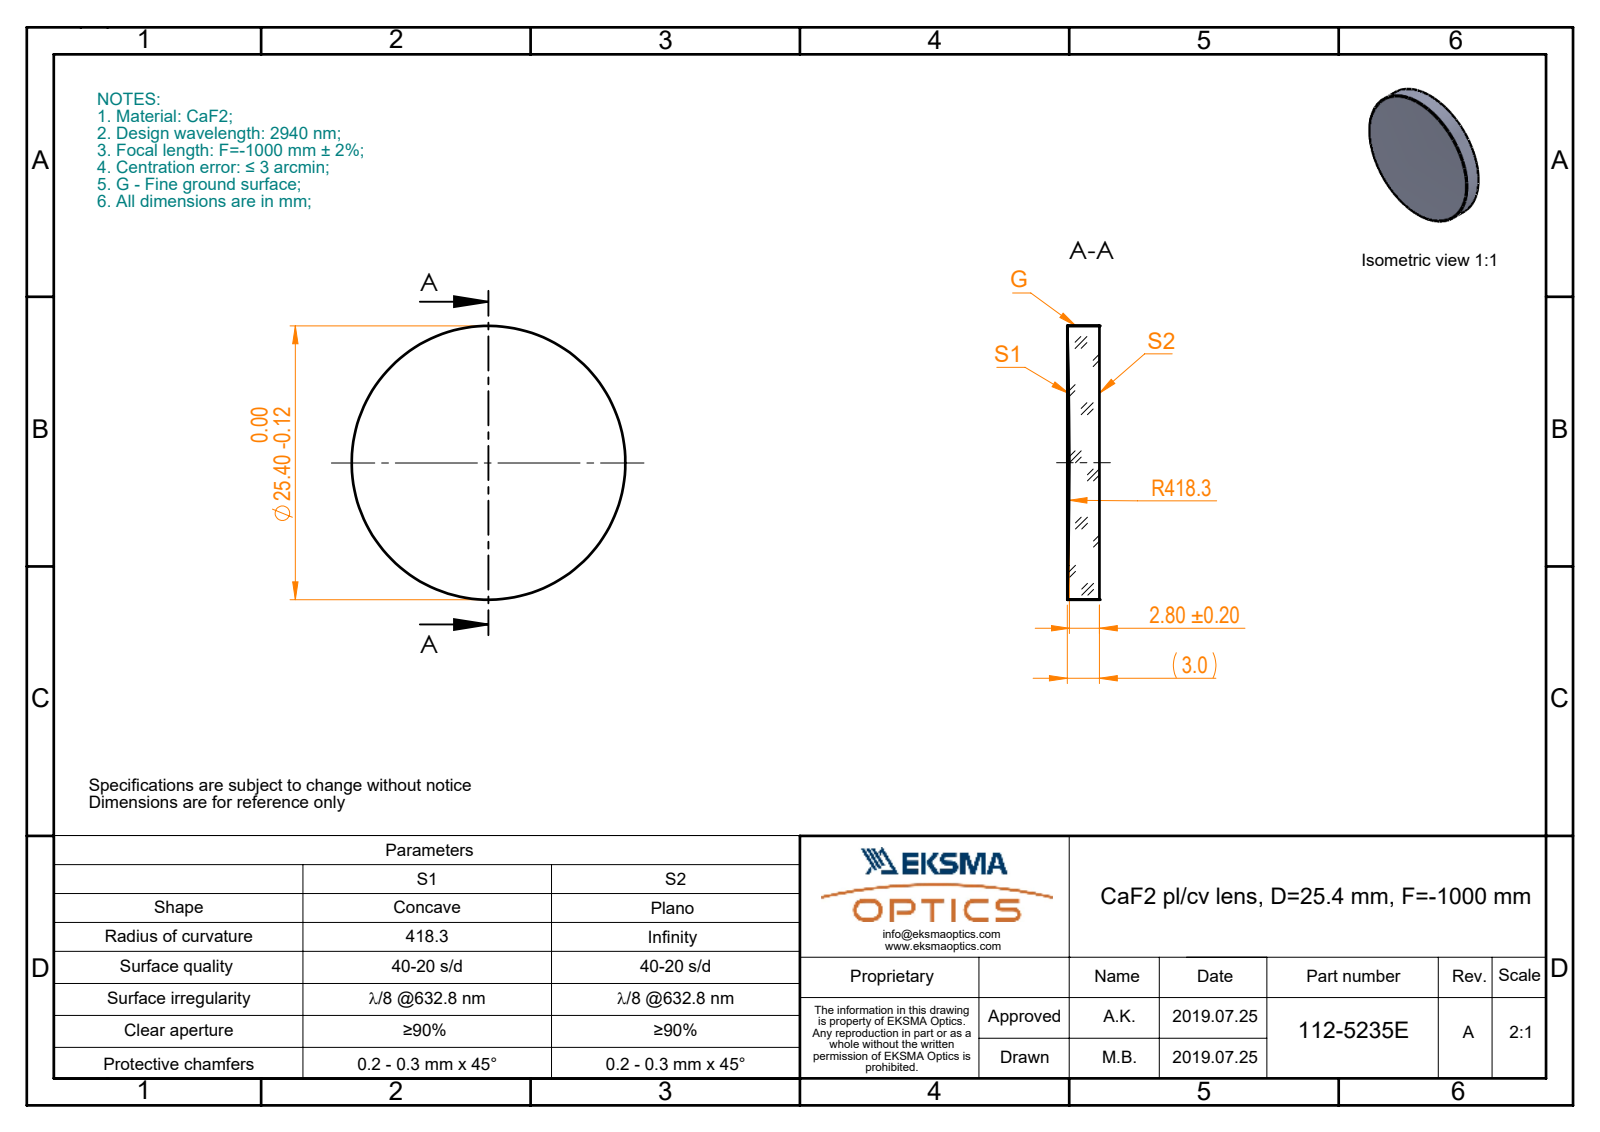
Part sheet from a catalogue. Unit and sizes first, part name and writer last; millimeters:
Units: millimetres
Overall size (bounding box): 25.4 × 25.4 × 2.99
Round bosses / shafts (diameter × count): ⌀25.4 ×1
Volume: 1 468 mm³ · Surface area: 1 252 mm²
Bodies: 1 solid, 5 faces (1 planar, 2 cylindrical, 2 other)
Part name (STEP PRODUCT): 112-5235E CaF2 pl-cv 12.7 F-1000
STEP written by: SolidWorks 2017 (CONFIG_CONTROL_DESIGN)
